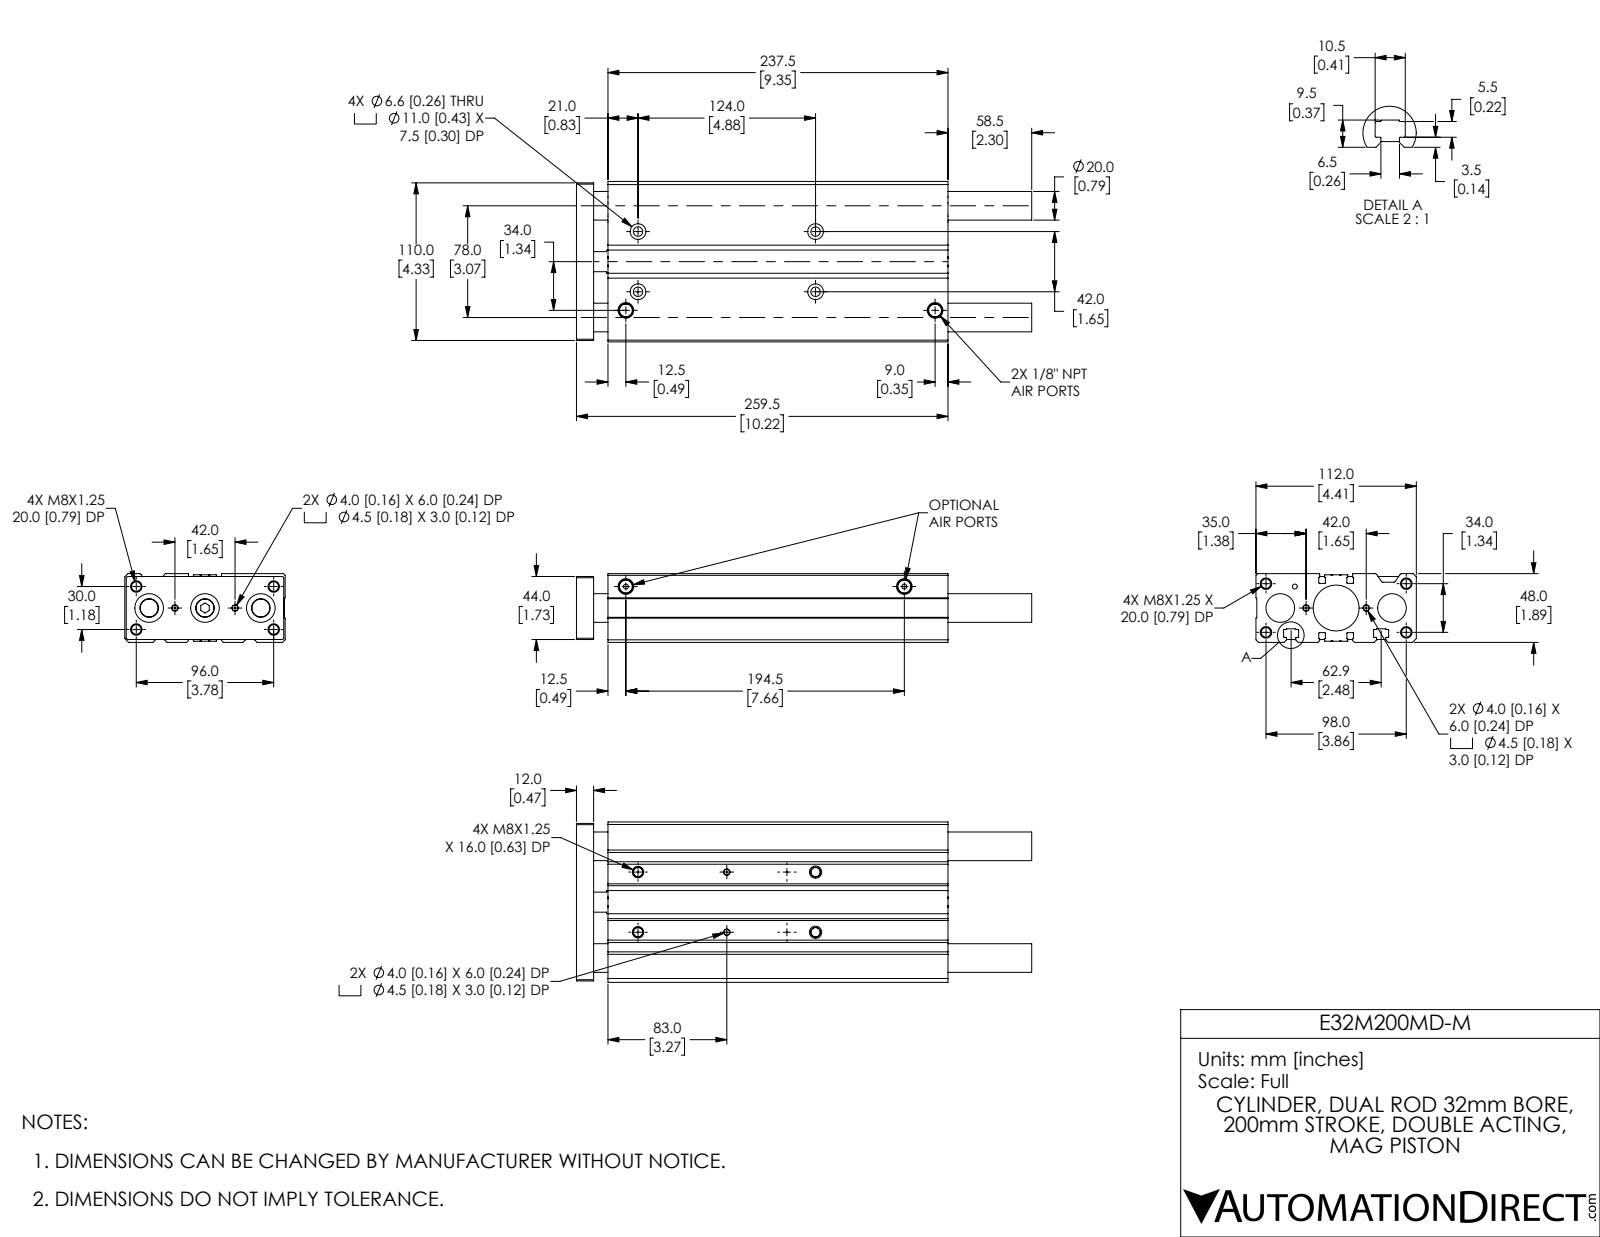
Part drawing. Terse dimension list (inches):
name: E32M200MD-M; E32M200MD-M_BODY; E32M200MD-M_ENDPLATE
written by: SolidWorks 2019 (CONFIG_CONTROL_DESIGN)
unit: in
bodies: 5 solids, 423 faces (139 planar, 190 cylindrical, 94 other)
size: 12.52 × 4.409 × 1.89
volume: 69.63 in³; area: 378.2 in²
holes: 12× ⌀0.262, 4× ⌀0.157, 4× ⌀0.177, 4× ⌀0.26, 4× ⌀0.433, 3× ⌀0.394, 3× ⌀0.787, 2× ⌀0.135, 2× ⌀0.51, 1× ⌀0.135, 1× ⌀0.787, 1× ⌀1.26
bosses: 1× ⌀0.63, 1× ⌀0.51
rounds: 32× R0.008, 28× R0.016, 4× R0.047, 2× R0.012
face distances: 1.89, 0.031, 0.236, 4.409, 1.858, 1.484, 1.622, 0.024, 1.516, 0.772
hole spacings: 0.088, 0.689, 0.776, 1.216, 1.261, 1.29, 1.654, 1.98
